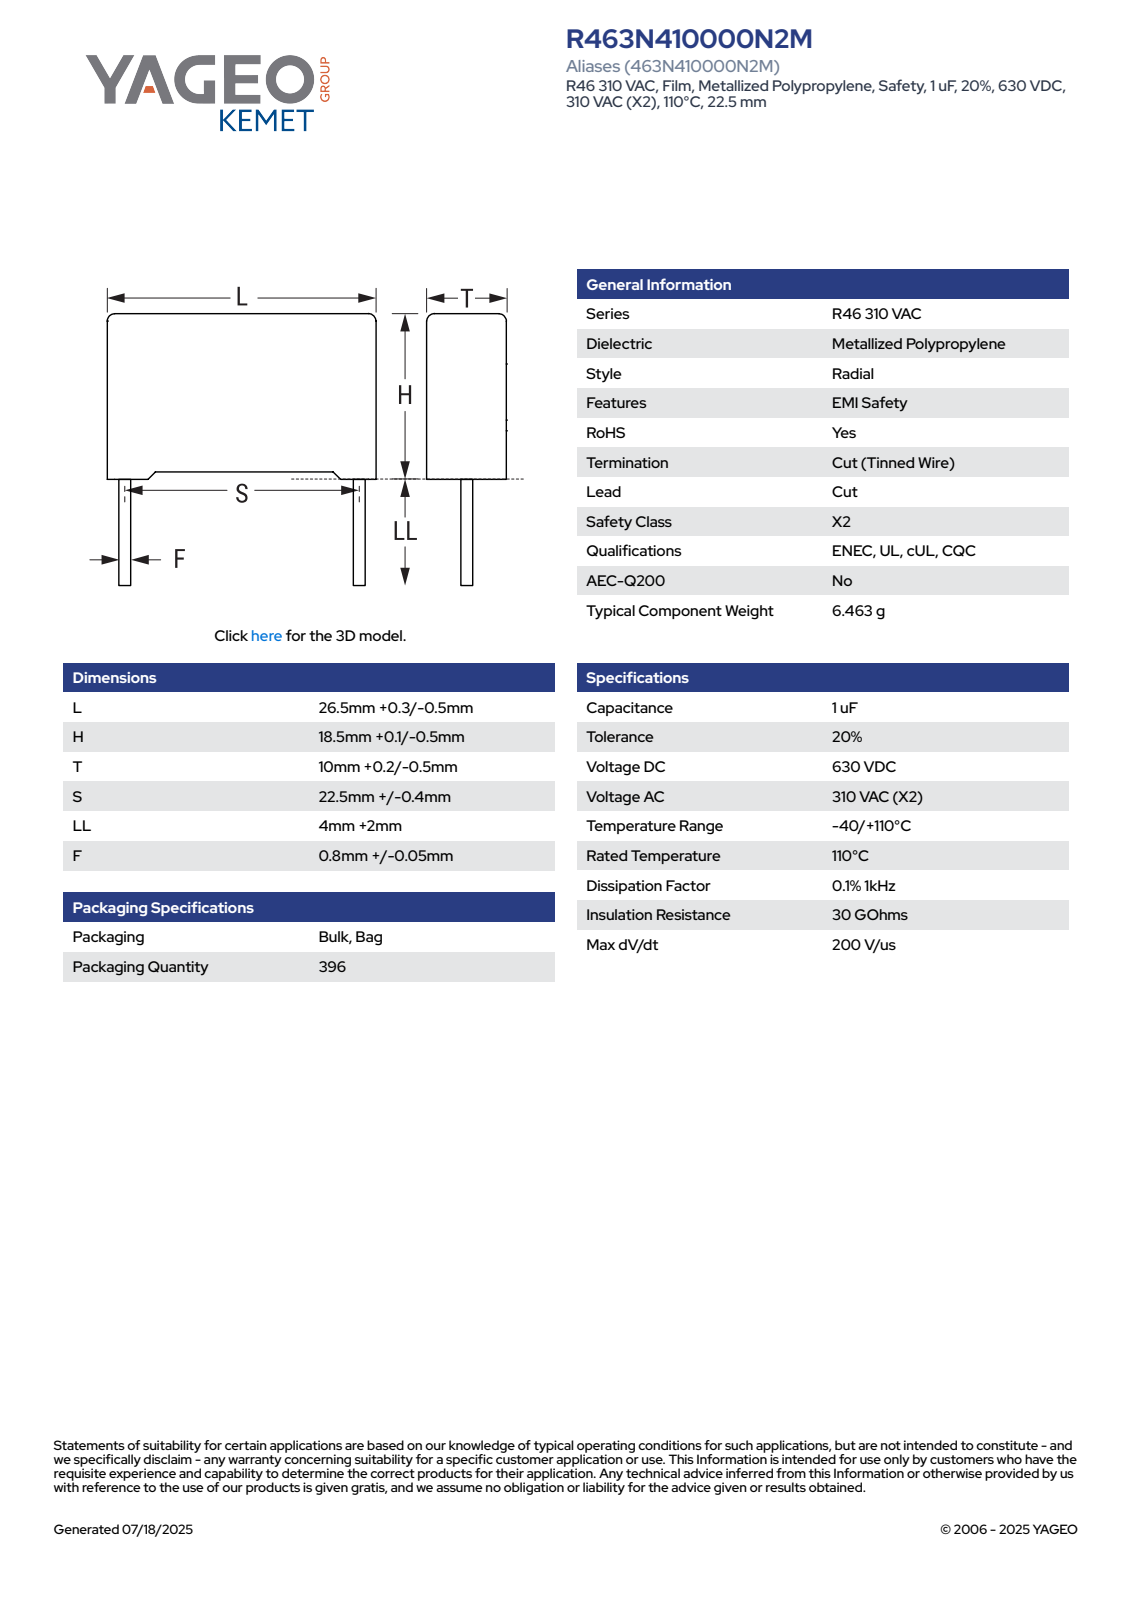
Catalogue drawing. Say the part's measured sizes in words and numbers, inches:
The part is named "CFR_RB2_26.5X18.5X10_L26.8H18.6T10.2S22.5LL6F0.85". Its 3-D file was written by "SolidWorks 2021 (AUTOMOTIVE_DESIGN)". It is 4 solids with 85 faces: 77 planar, 8 cylindrical and 0 other. Overall it measures 1.055 by 0.969 by 0.402 inches. Its volume is 0.3 cubic inches and its surface area 3.1 square inches. Round bosses or shafts: 2 of diameter 0.033. Partial cylindrical surfaces (rounded edges, fillets, slot ends): 4 of radius 0.02. The main face-to-face distances are 0.402, 0.703, 1.055, 0.707, 0.03, 0.025, 0.732, 0.035, 0.367, 1.02.
